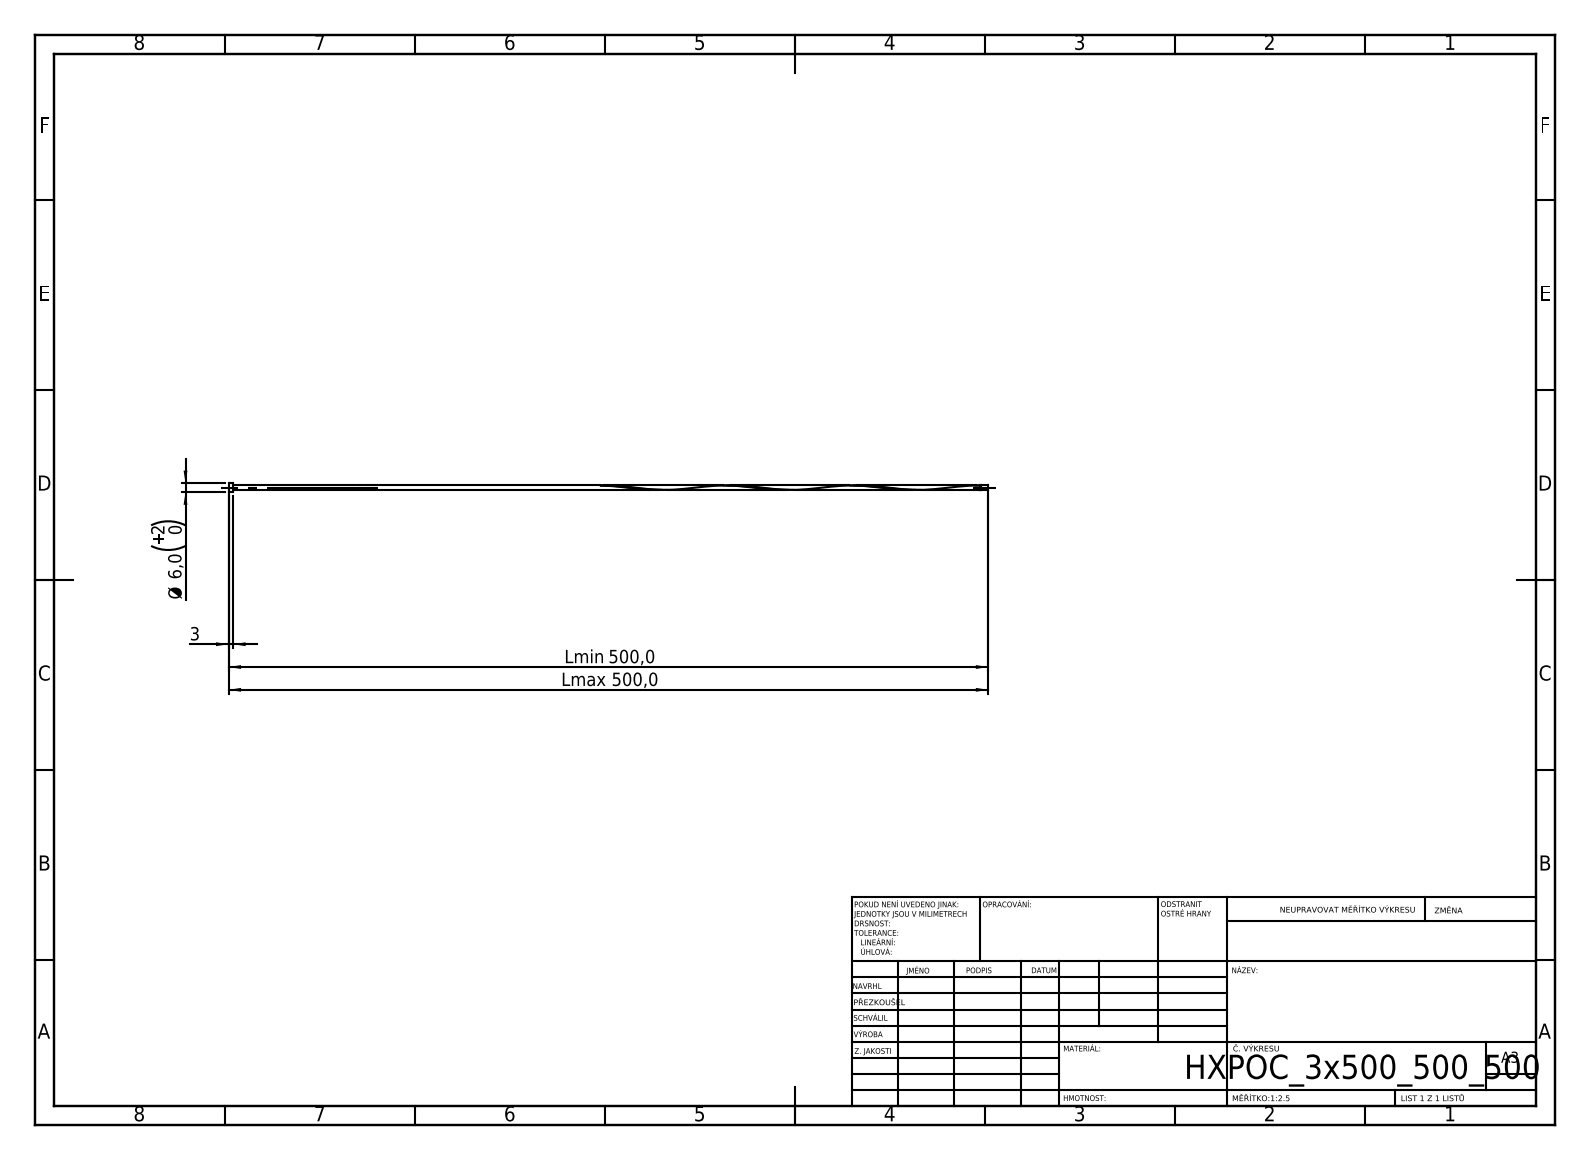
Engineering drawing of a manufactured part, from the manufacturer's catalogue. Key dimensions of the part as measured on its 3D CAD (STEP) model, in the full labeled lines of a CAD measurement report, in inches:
STEP written by: SolidWorks 2019 (CONFIG_CONTROL_DESIGN)
Units: inches
Bodies: 1 solid, 16 faces (6 planar, 9 cylindrical, 1 other)
Overall size (bounding box): 19.685 × 0.236 × 0.236
Volume: 0.265 in³ · Surface area: 9.987 in²
Round bosses / shafts (diameter × count): ⌀0.236 ×1, ⌀0.118 ×1, ⌀0.094 ×1
Main face-to-face distances: 0.118, 19.685, 19.567, 19.487, 19.369, 0.198, 19.463, 19.345, 0.024, 0.222
